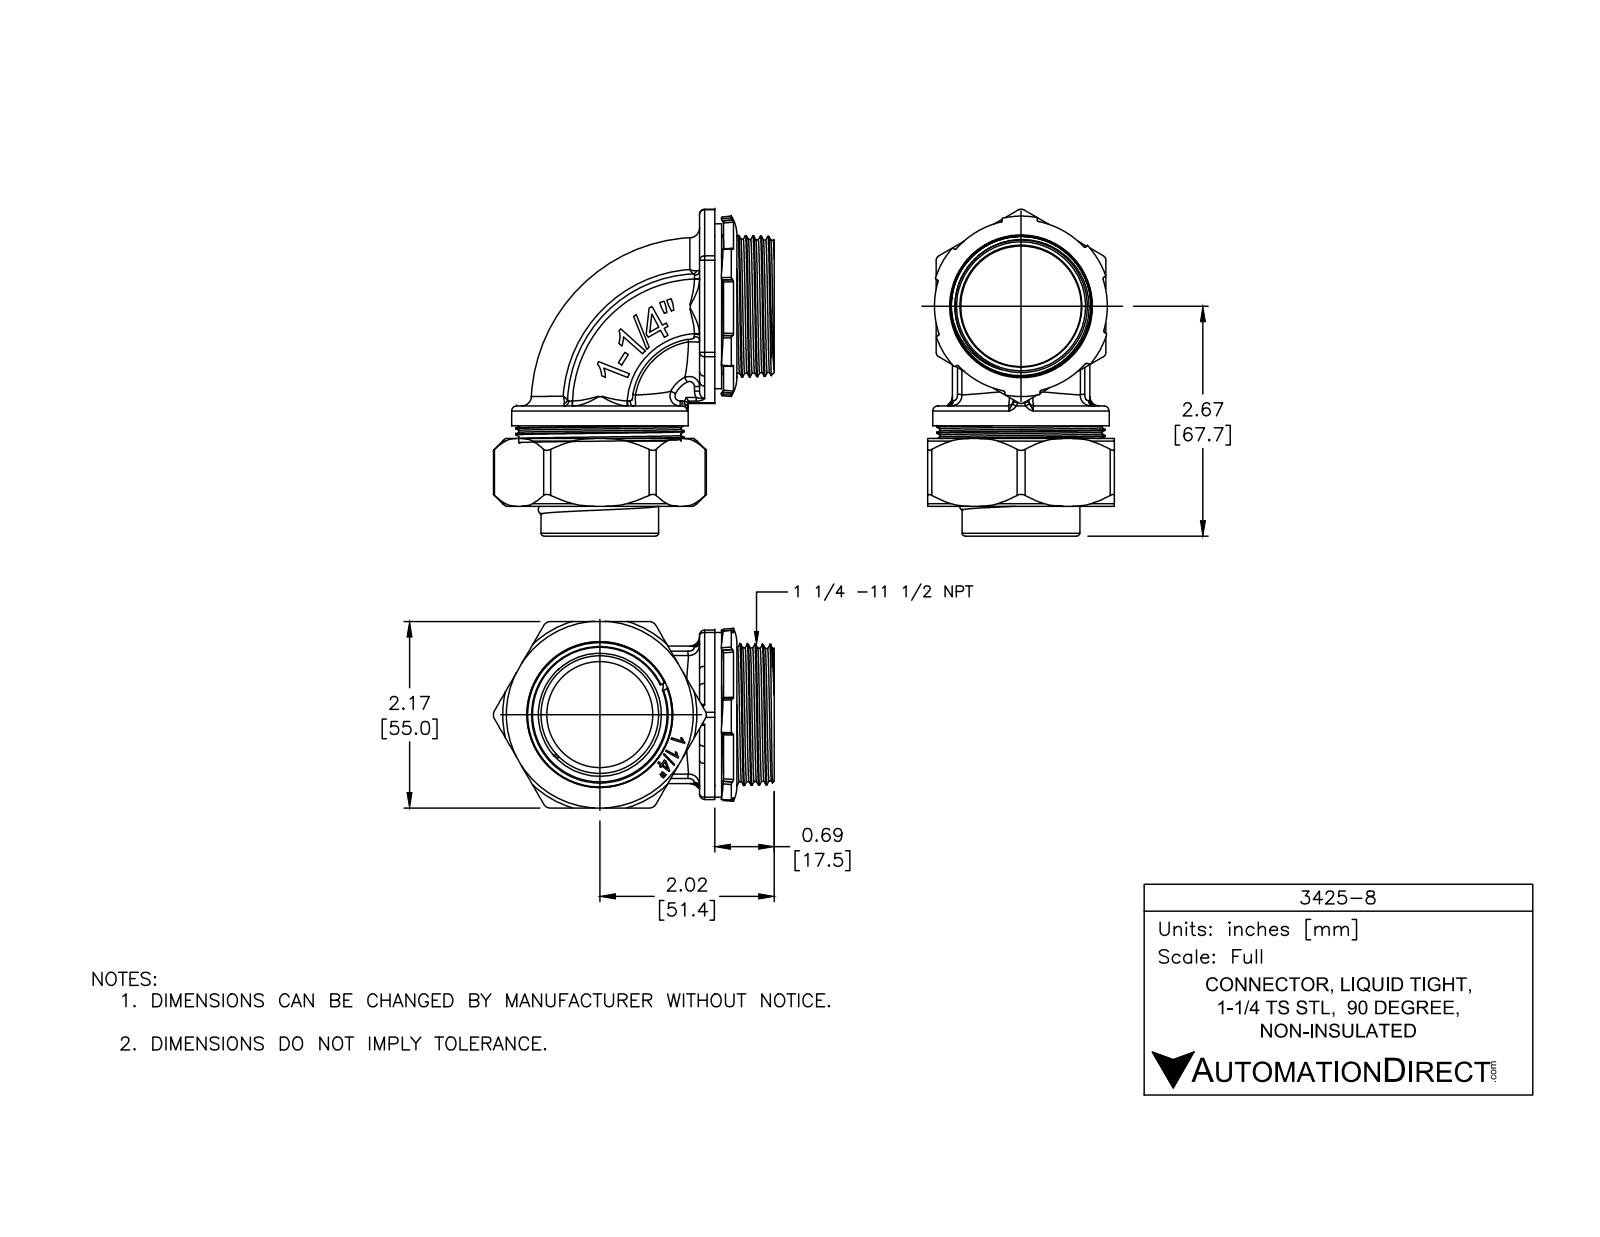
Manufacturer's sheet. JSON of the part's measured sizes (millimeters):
{"part_name": "3425-8", "step_written_by": "SolidWorks 2018 (AUTOMOTIVE_DESIGN)", "units": "millimeters", "bodies": {"solids": 6, "faces": 678, "planar": 271, "cylindrical": 123, "other": 284}, "overall_size": [96.4, 82.8, 55], "volume_mm3": 60600, "surface_area_mm2": 55720, "round_holes": [[35.5, 2], [4.6, 1], [31.3, 1], [33, 1], [36, 1], [39.5, 1], [41.6, 1], [42.3, 1], [43, 1], [44.7, 1], [48.5, 1]], "round_bosses_or_shafts": [[52, 1], [49.6, 1], [48.6, 1], [47.5, 1], [44, 1], [34.7, 1], [33, 1], [3.8, 1]], "partial_cylinders_radius": [[1.5, 16], [0.3, 8], [2.4, 6], [0.1, 2], [1.2, 2], [1.3, 2], [0.2, 1], [0.4, 1]], "face_to_face_distances": [55, 7.2, 47.8, 23.7, 40.5, 2, 20, 9.6, 50, 4.5], "hole_center_spacings": [24.5]}
